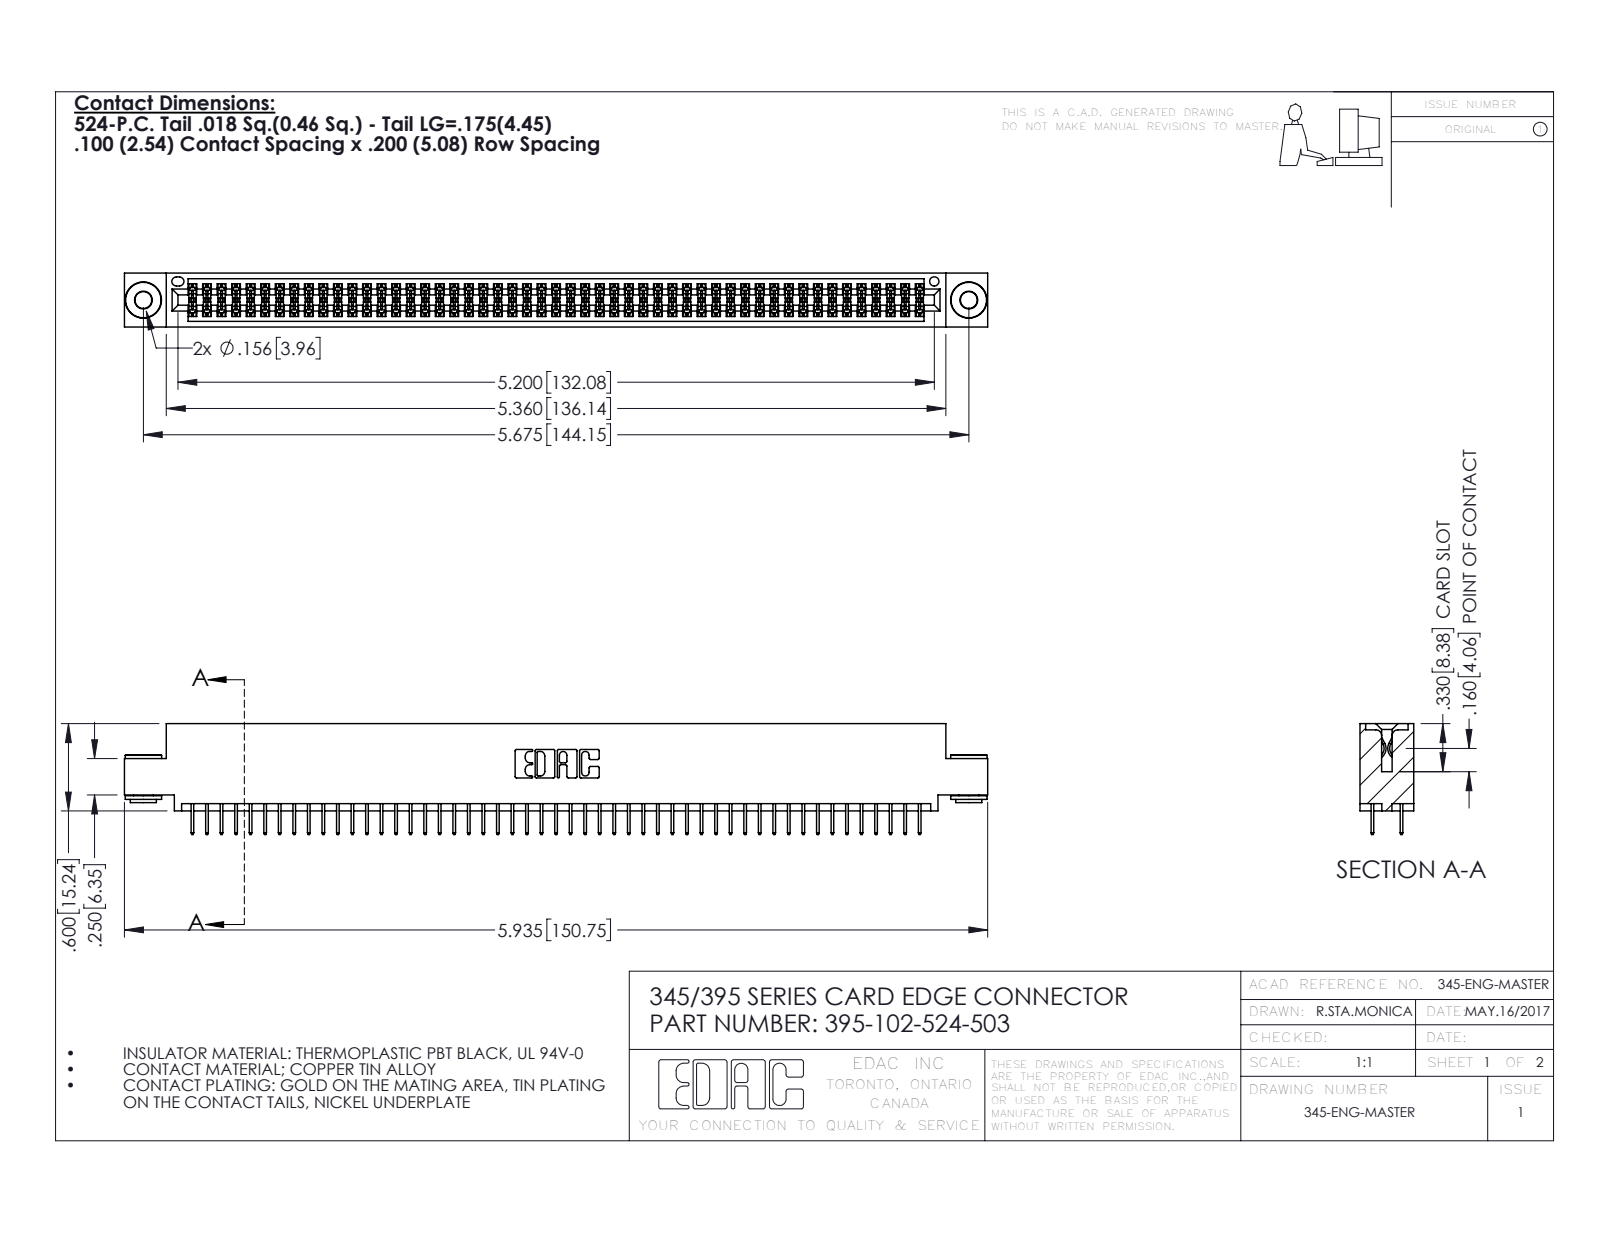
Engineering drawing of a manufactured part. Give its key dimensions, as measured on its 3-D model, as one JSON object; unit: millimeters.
{"part_name": "345-250-002_345-250-002-102; 345 Part_0.110 Offset - 0.156 Dia-TH; 395-102-524-503; 345-292-001_345-293-124", "step_written_by": "SolidWorks 2016 (CONFIG_CONTROL_DESIGN)", "units": "millimeters", "bodies": {"solids": 105, "faces": 5676, "planar": 4072, "cylindrical": 1596, "other": 8}, "overall_size": [150.7, 19.4, 9.4], "volume_mm3": 14500, "surface_area_mm2": 21530, "round_holes": [[2.9, 2], [4, 2], [1.6, 1]], "round_bosses_or_shafts": [[6.4, 2], [4.6, 2], [3.5, 2]], "partial_cylinders_radius": [[0.2, 153], [0.3, 22], [0.2, 6], [0.8, 6], [0.7, 3], [0.4, 2], [0.5, 2], [0.6, 2]], "face_to_face_distances": [1.8, 7.6, 5.1, 9.4, 0.6, 2.5, 6.9, 5.7, 1.8, 4.4], "hole_center_spacings": [6.9, 138.2, 144.1]}
